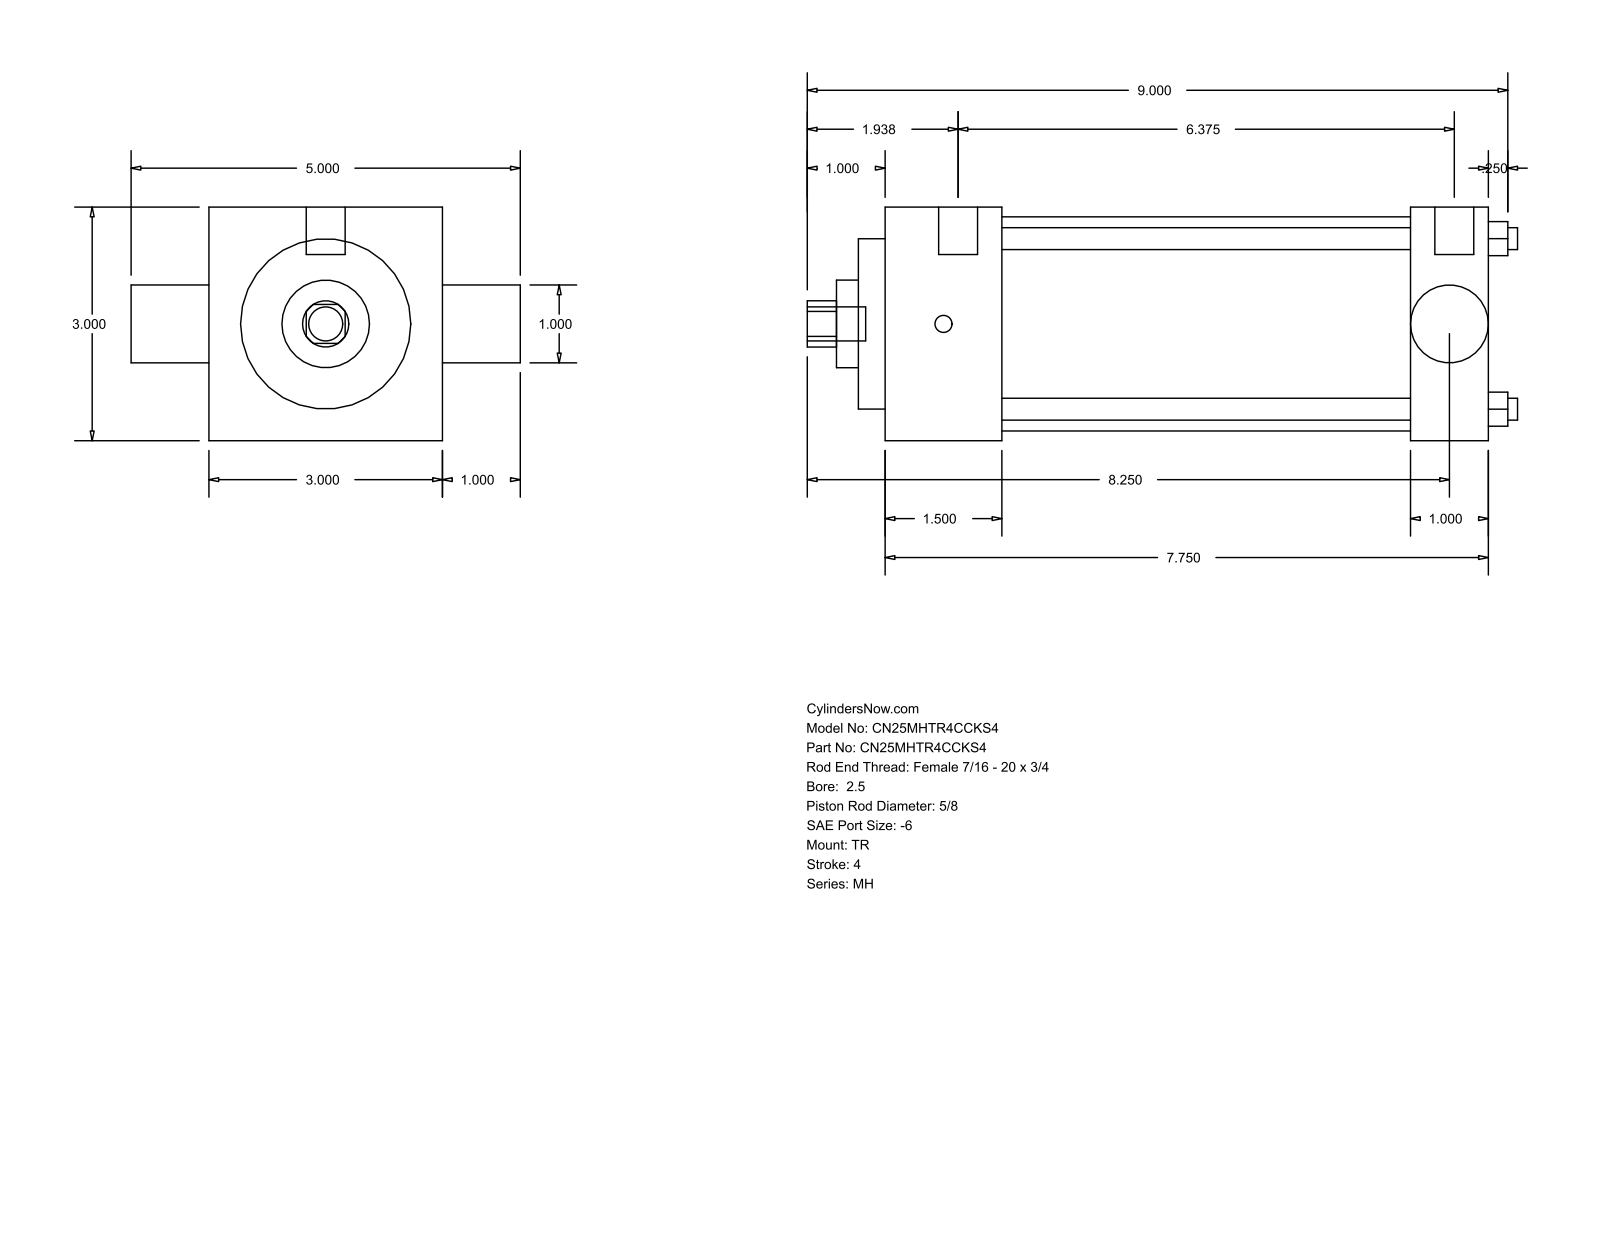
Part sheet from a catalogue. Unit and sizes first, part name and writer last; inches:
Units: inches
Overall size (bounding box): 9.125 × 5 × 3
Round holes (diameter × count): ⌀0.281 ×4, ⌀0.625 ×1, ⌀0.998 ×1, ⌀1.125 ×1, ⌀2.187 ×1, ⌀2.75 ×1
Round bosses / shafts (diameter × count): ⌀0.219 ×3, ⌀0.5 ×2, ⌀0.437 ×1
Partial cylindrical surfaces — rounded edges, fillets, slot ends (radius × count): R0.297 ×1
Main face-to-face distances: 3, 7.75, 1, 1.5, 6.25, 6.75, 5.25, 0.344, 1.844, 7.094
Hole centre spacings: 1.548, 2.19, 3.097
Bodies: 0 solids, 86 faces (61 planar, 25 cylindrical, 0 other)
Part name (STEP PRODUCT): MH_TR__0250_0.625
STEP written by: GSSL Pune (CONFIG_CONTROL_DESIGN)
